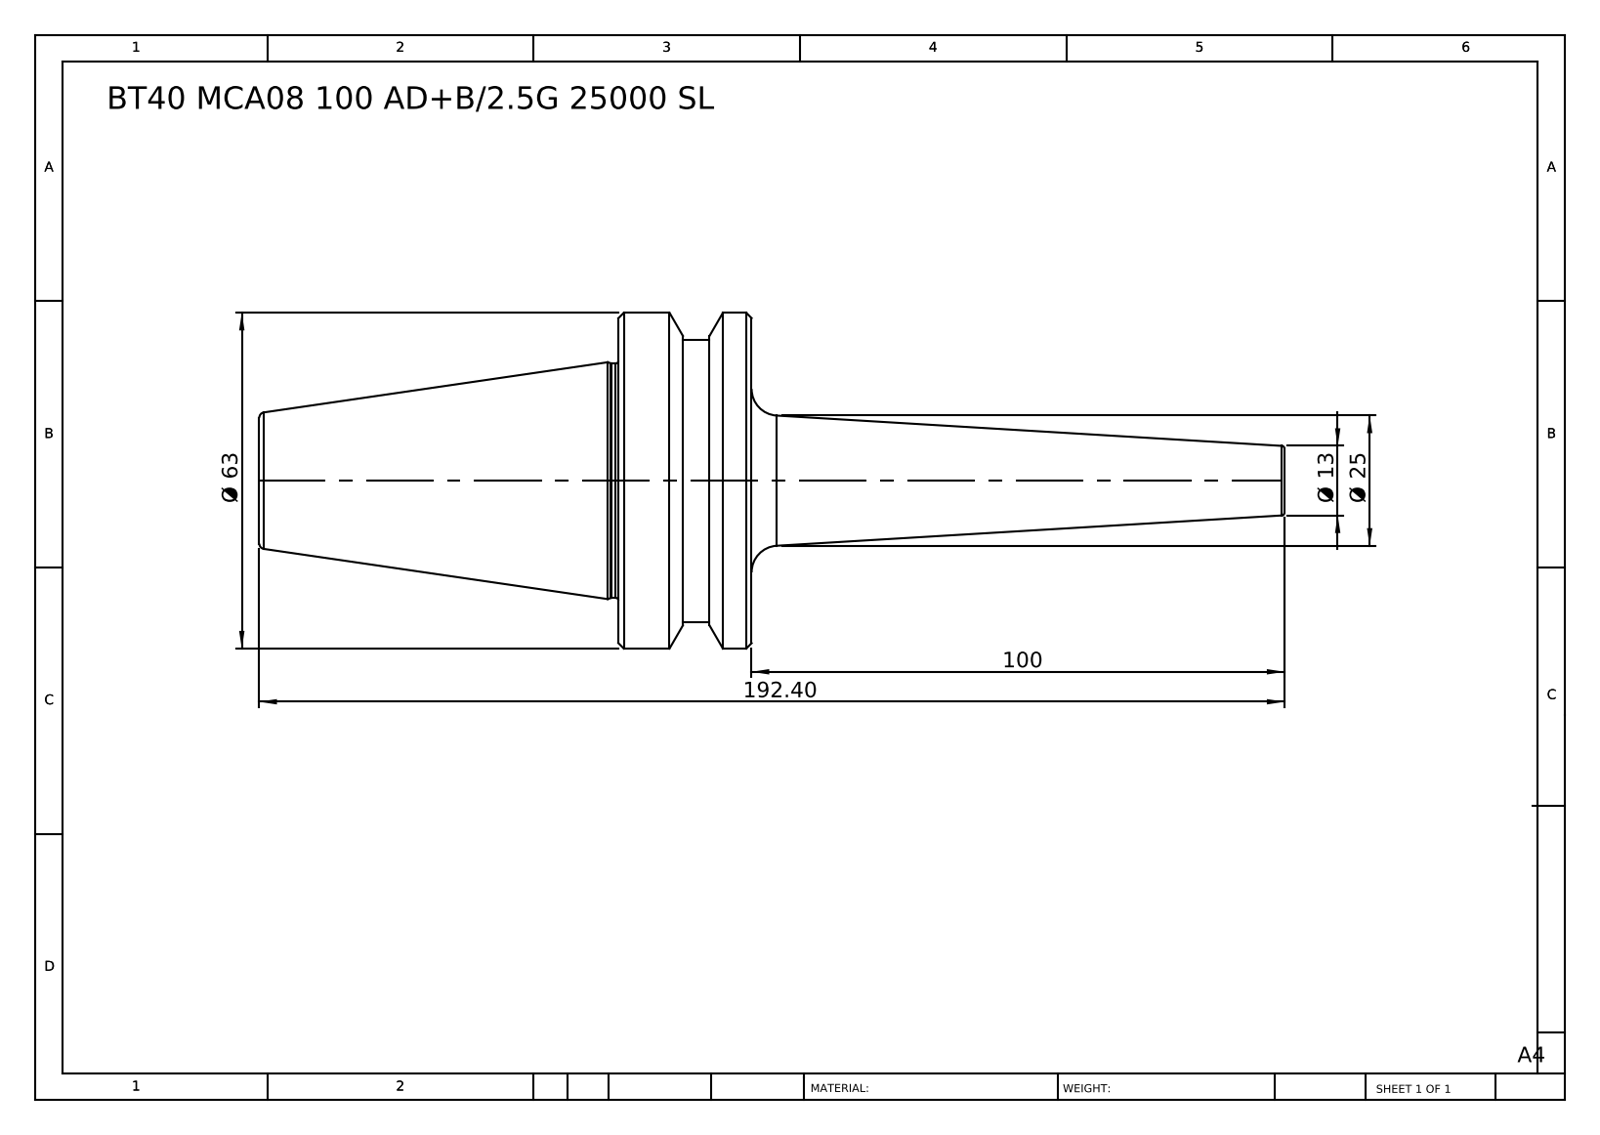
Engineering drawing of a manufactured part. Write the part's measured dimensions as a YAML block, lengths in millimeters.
part_name: "BT40 MCA08 100 AD+B-2.5G 25000 SL"
step_written_by: "SolidWorks 2014 (CONFIG_CONTROL_DESIGN)"
units: millimeters
bodies: {solids: 1, faces: 38, planar: 6, cylindrical: 8, other: 24}
overall_size: [192.4, 63, 63]
volume: 168035
surface_area: 23810
round_bosses_or_shafts:
  - {diameter: 63, count: 1}
  - {diameter: 53, count: 1}
  - {diameter: 44, count: 1}
face_to_face_distances: [25, 92.4, 67.4, 100, 125, 192.4, 112.9, 12.9, 12.1, 79.5]
